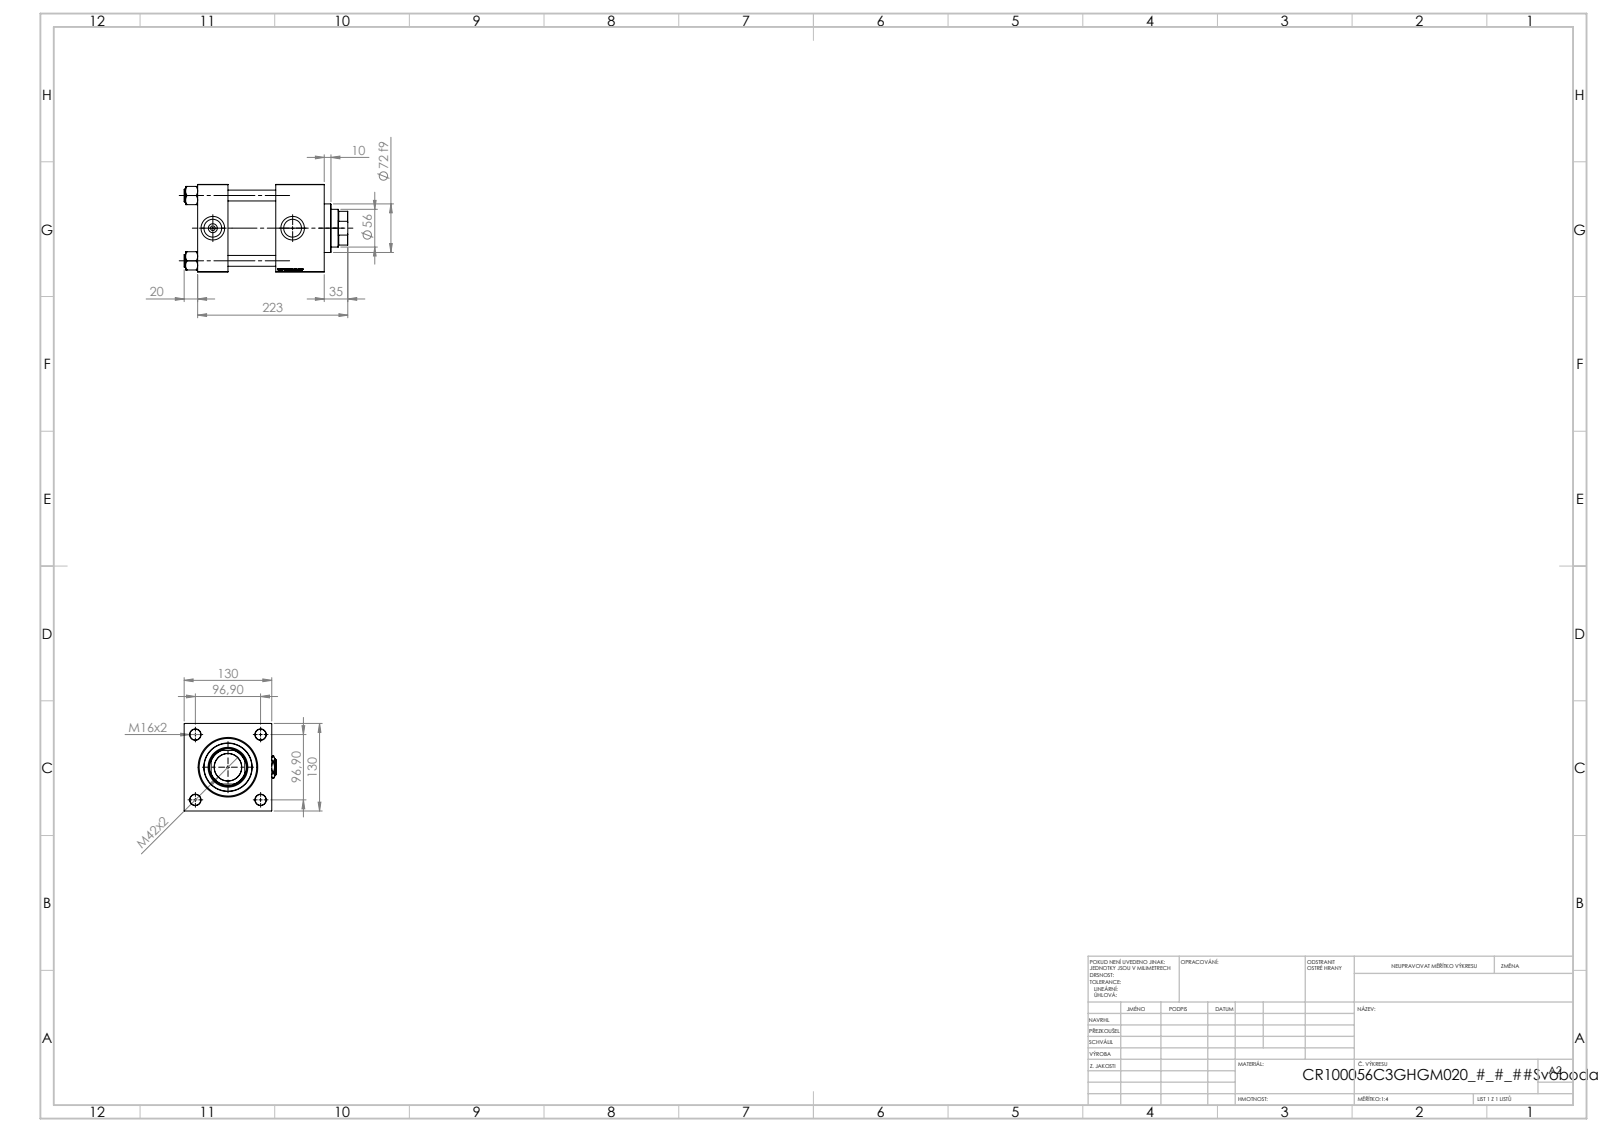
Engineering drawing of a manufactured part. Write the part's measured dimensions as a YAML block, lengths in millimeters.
part_name: "V215CR_C_TYCINKA; Zatka_pro_OIL_PORT; NUT_M5_C; V215CR_VCP_C (+2 more)"
step_written_by: "SolidWorks 2019 (CONFIG_CONTROL_DESIGN)"
units: millimeters
bodies: {solids: 13, faces: 1297, planar: 621, cylindrical: 98, other: 578}
overall_size: [243, 137, 130]
volume: 2461000
surface_area: 340431
round_holes:
  - {diameter: 16, count: 4}
  - {diameter: 7, count: 2}
  - {diameter: 26.44, count: 2}
  - {diameter: 35, count: 2}
  - {diameter: 40.5, count: 1}
  - {diameter: 56, count: 1}
  - {diameter: 59, count: 1}
  - {diameter: 76, count: 1}
  - {diameter: 85.5, count: 1}
  - {diameter: 100, count: 1}
round_bosses_or_shafts:
  - {diameter: 19, count: 4}
  - {diameter: 106, count: 1}
  - {diameter: 72, count: 1}
partial_cylinders:
  - {radius: 27, count: 1}
face_to_face_distances: [130, 45, 188, 143, 116, 71, 72, 20, 51, 92]
hole_center_spacings: [68.52, 96.9, 137.04, 118.5]
